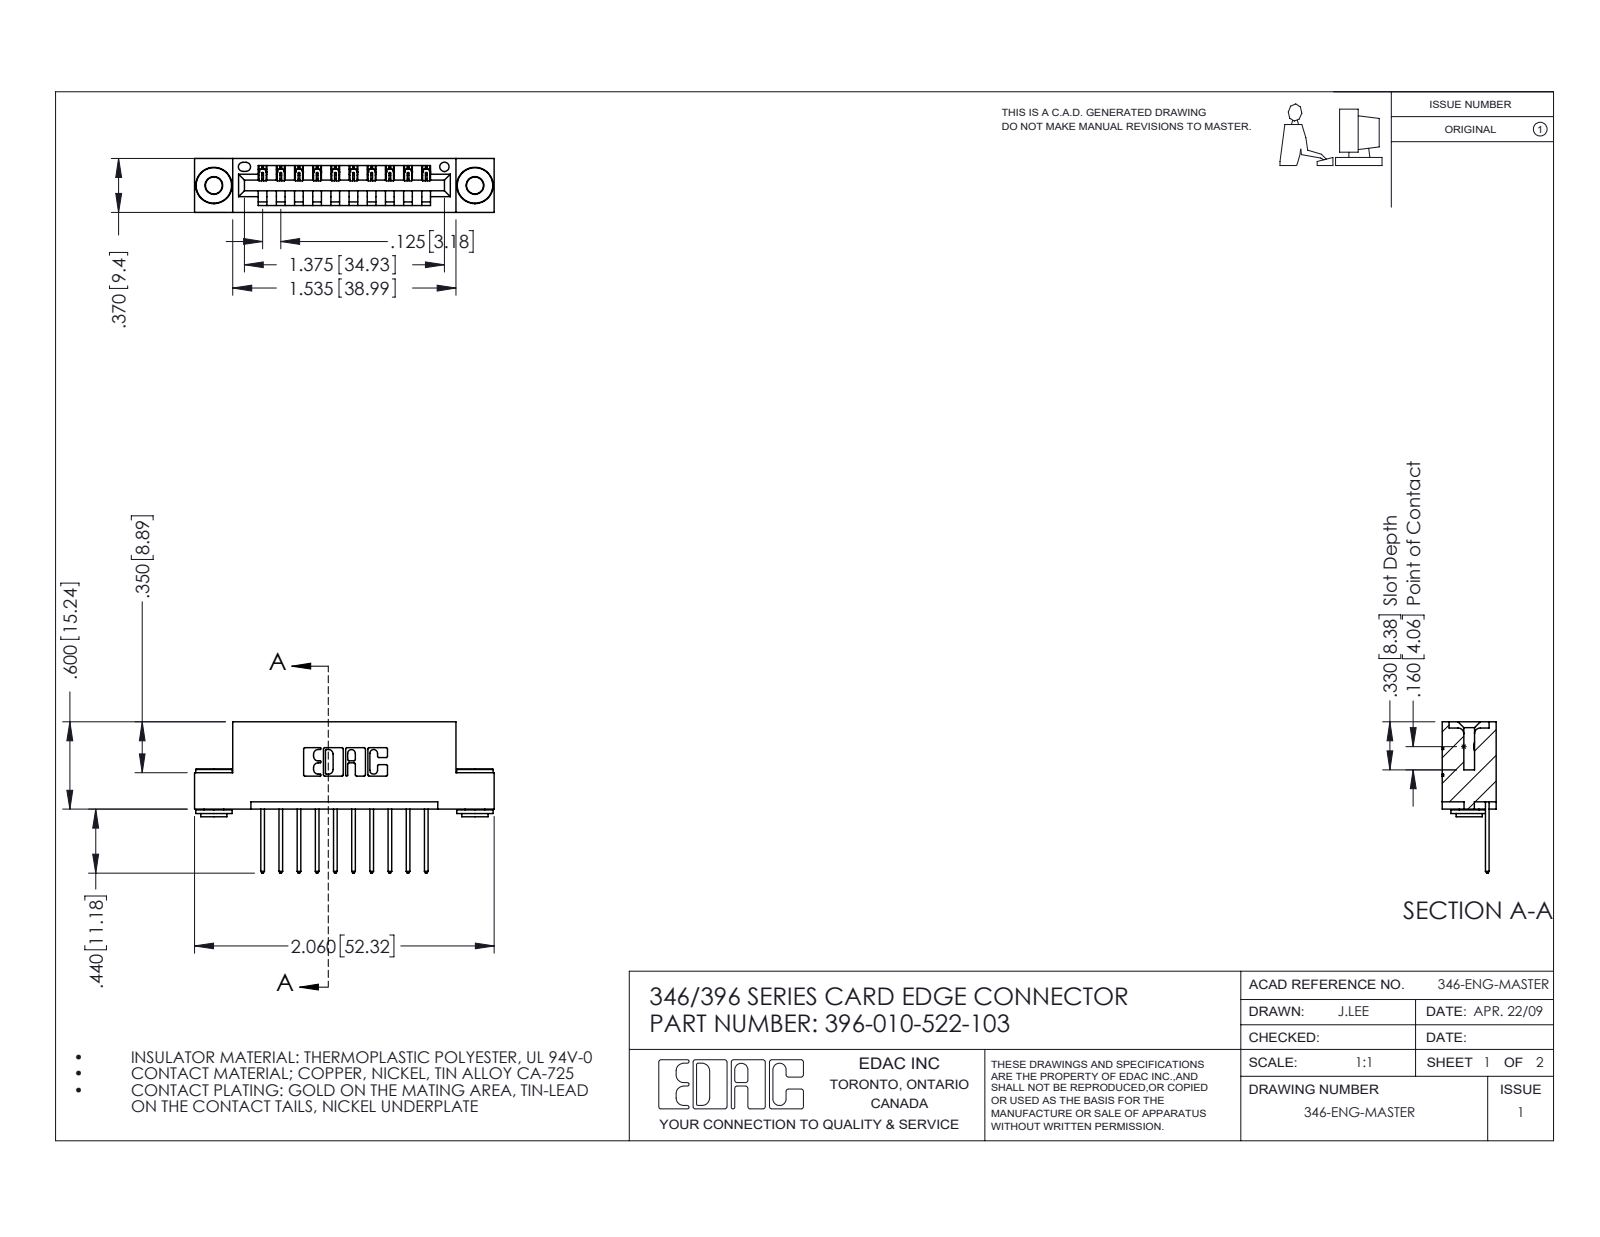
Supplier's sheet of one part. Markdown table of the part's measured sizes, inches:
| quantity | value |
| --- | --- |
| part name | 346 Part_Flush Mounting Lugs - 0.156 Dia-TH; 396-010-522-103; 345-292-001_345-293-122; 345-250-002_345-250-002-102 |
| STEP written by | SolidWorks 2016 (CONFIG_CONTROL_DESIGN) |
| units | inches |
| bodies | 13 solids, 740 faces (486 planar, 246 cylindrical, 8 other) |
| overall size | 2.06 × 1.04 × 0.37 |
| volume | 0.293 in³ |
| surface area | 9.178 in² |
| round holes (diameter × count) | 0.116 × 2, 0.156 × 2, 0.064 × 1 |
| round bosses / shafts (diameter × count) | 0.25 × 2, 0.18 × 2, 0.136 × 2 |
| partial cylindrical surfaces (radius × count) | 0.01 × 22, 0.006 × 20, 0.01 × 20, 0.007 × 6, 0.031 × 6, 0.026 × 3, 0.031 × 2, 0.04 × 2 |
| main face-to-face distances | 0.25, 0.048, 0.322, 0.37, 0.025, 0.072, 0.298, 0.148, 0.222, 0.1 |
| hole center spacings | 0.246, 1.59, 1.795 |
